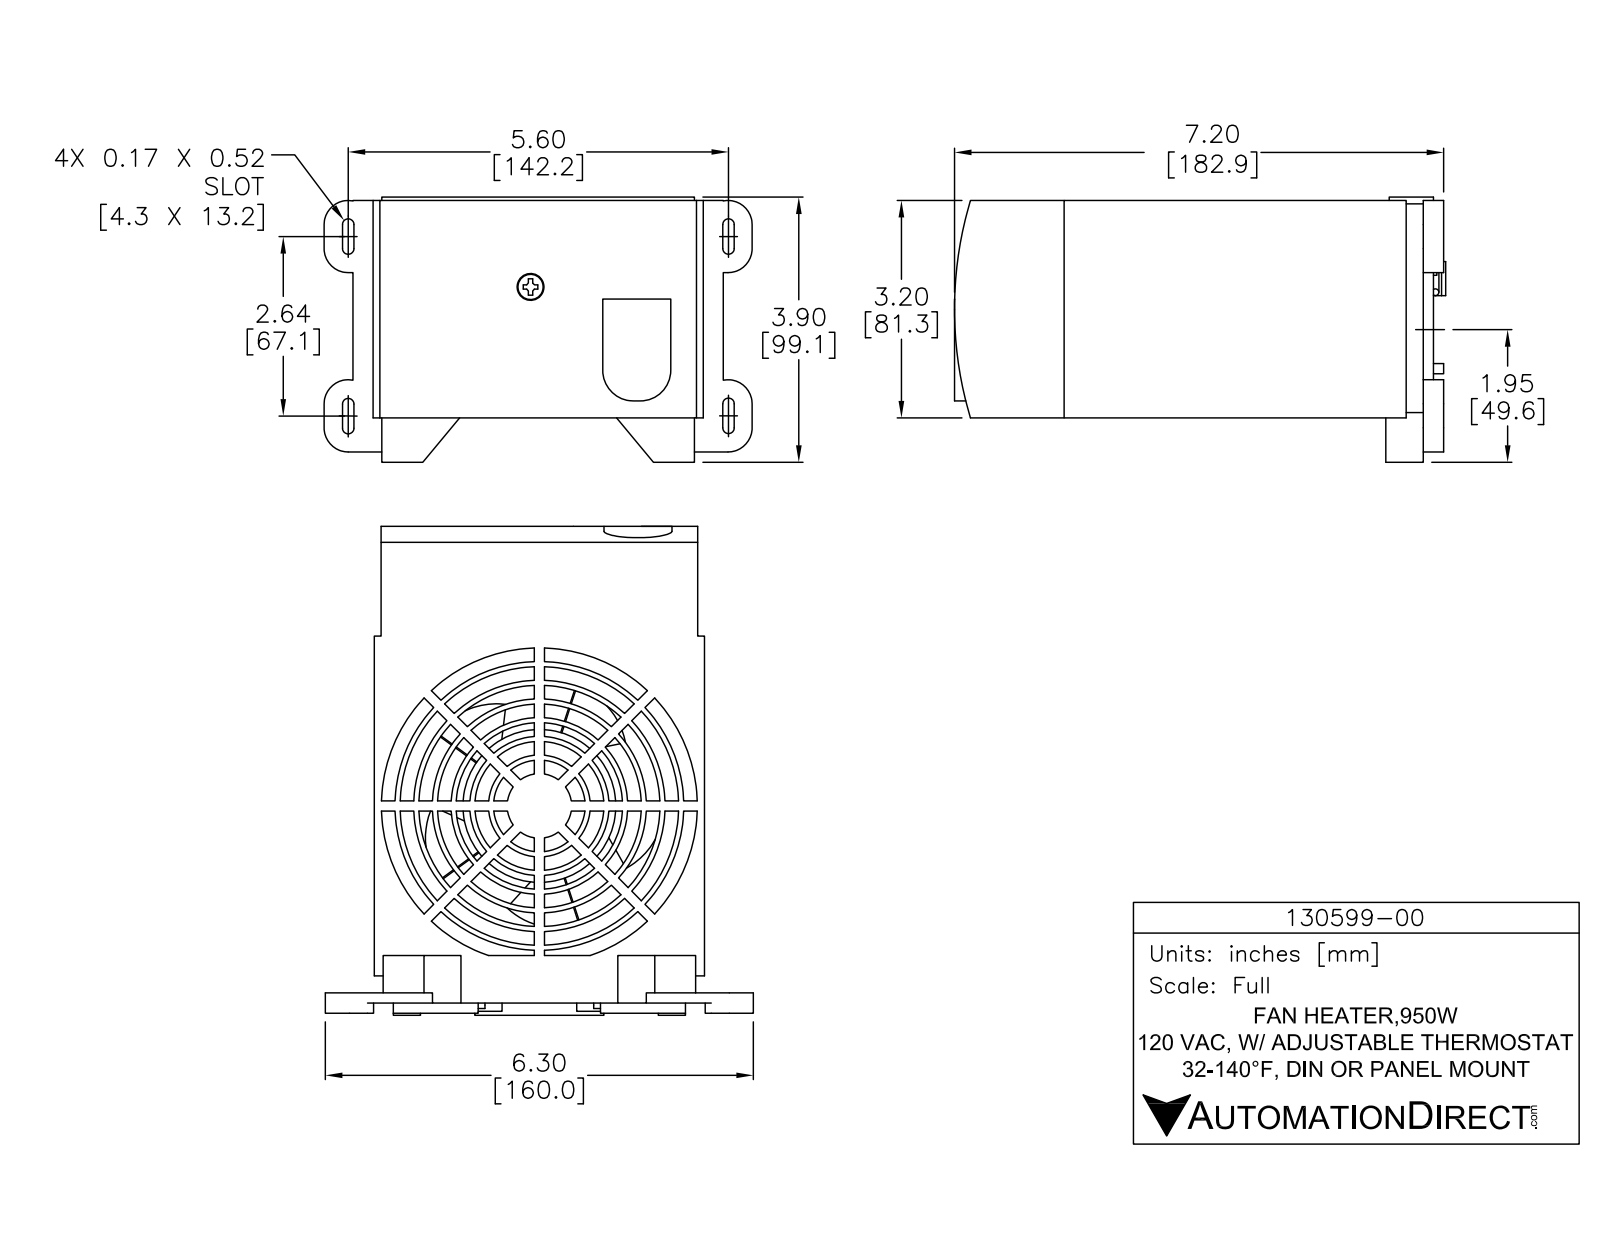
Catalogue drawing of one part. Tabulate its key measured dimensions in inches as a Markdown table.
| quantity | value |
| --- | --- |
| part name | 130599-00 |
| STEP written by | SolidWorks 2013 (AUTOMOTIVE_DESIGN) |
| units | inches |
| bodies | 1 solid, 716 faces (434 planar, 253 cylindrical, 29 other) |
| overall size | 7.13 × 6.16 × 3.922 |
| volume | 98.11 in³ |
| surface area | 250.4 in² |
| round holes (diameter × count) | 0.31 × 1, 0.36 × 1 |
| round bosses / shafts (diameter × count) | 0.375 × 1, 0.238 × 1 |
| partial cylindrical surfaces (radius × count) | 0.07 × 84, 0.04 × 42, 0.325 × 16, 0.125 × 8, 0.252 × 8, 0.03 × 4, 0.06 × 4, 0.1 × 2 |
| main face-to-face distances | 4.95, 0.015, 0.305, 0.32, 0.22, 0.06, 2.782, 2.722, 3.032, 2.972 |
